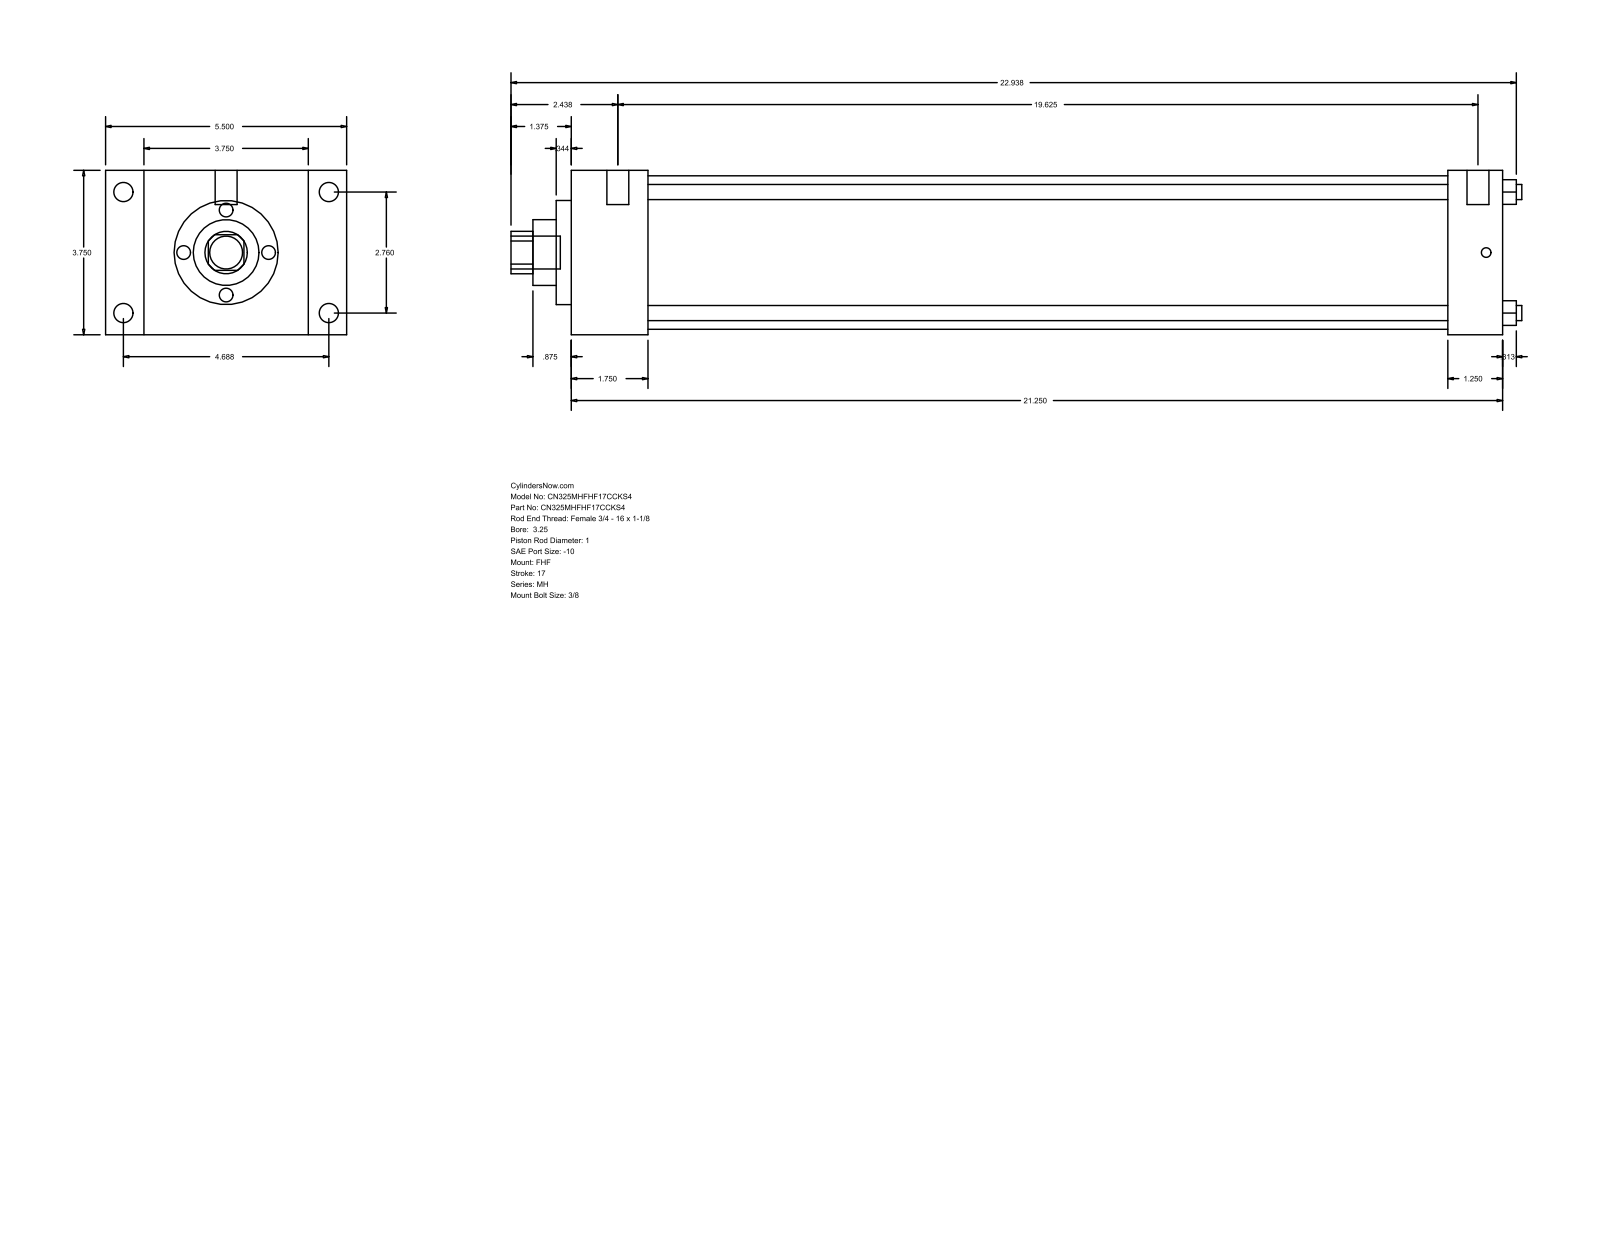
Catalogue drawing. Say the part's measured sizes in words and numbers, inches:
The part is named "MH_FHF__0325_1". Its 3-D file was written by "GSSL Pune (CONFIG_CONTROL_DESIGN)". It is 0 solids with 90 faces: 61 planar, 29 cylindrical and 0 other. Overall it measures 23.063 by 5.5 by 3.75 inches. Round holes: 4 of diameter 0.345, 1 of diameter 1, 1 of diameter 1.5, 1 of diameter 2.375, 1 of diameter 3.5. Round bosses or shafts: 4 of diameter 0.438, 4 of diameter 0.219, 2 of diameter 0.5, 1 of diameter 0.75. Partial cylindrical surfaces (rounded edges, fillets, slot ends): 1 of radius 0.484. The main face-to-face distances are 3.75, 21.25, 1.75, 19.5, 0.875, 4.625, 5.5, 20, 18.25, 1.25. The hole center spacings are 1.952, 2.76, 3.903.
